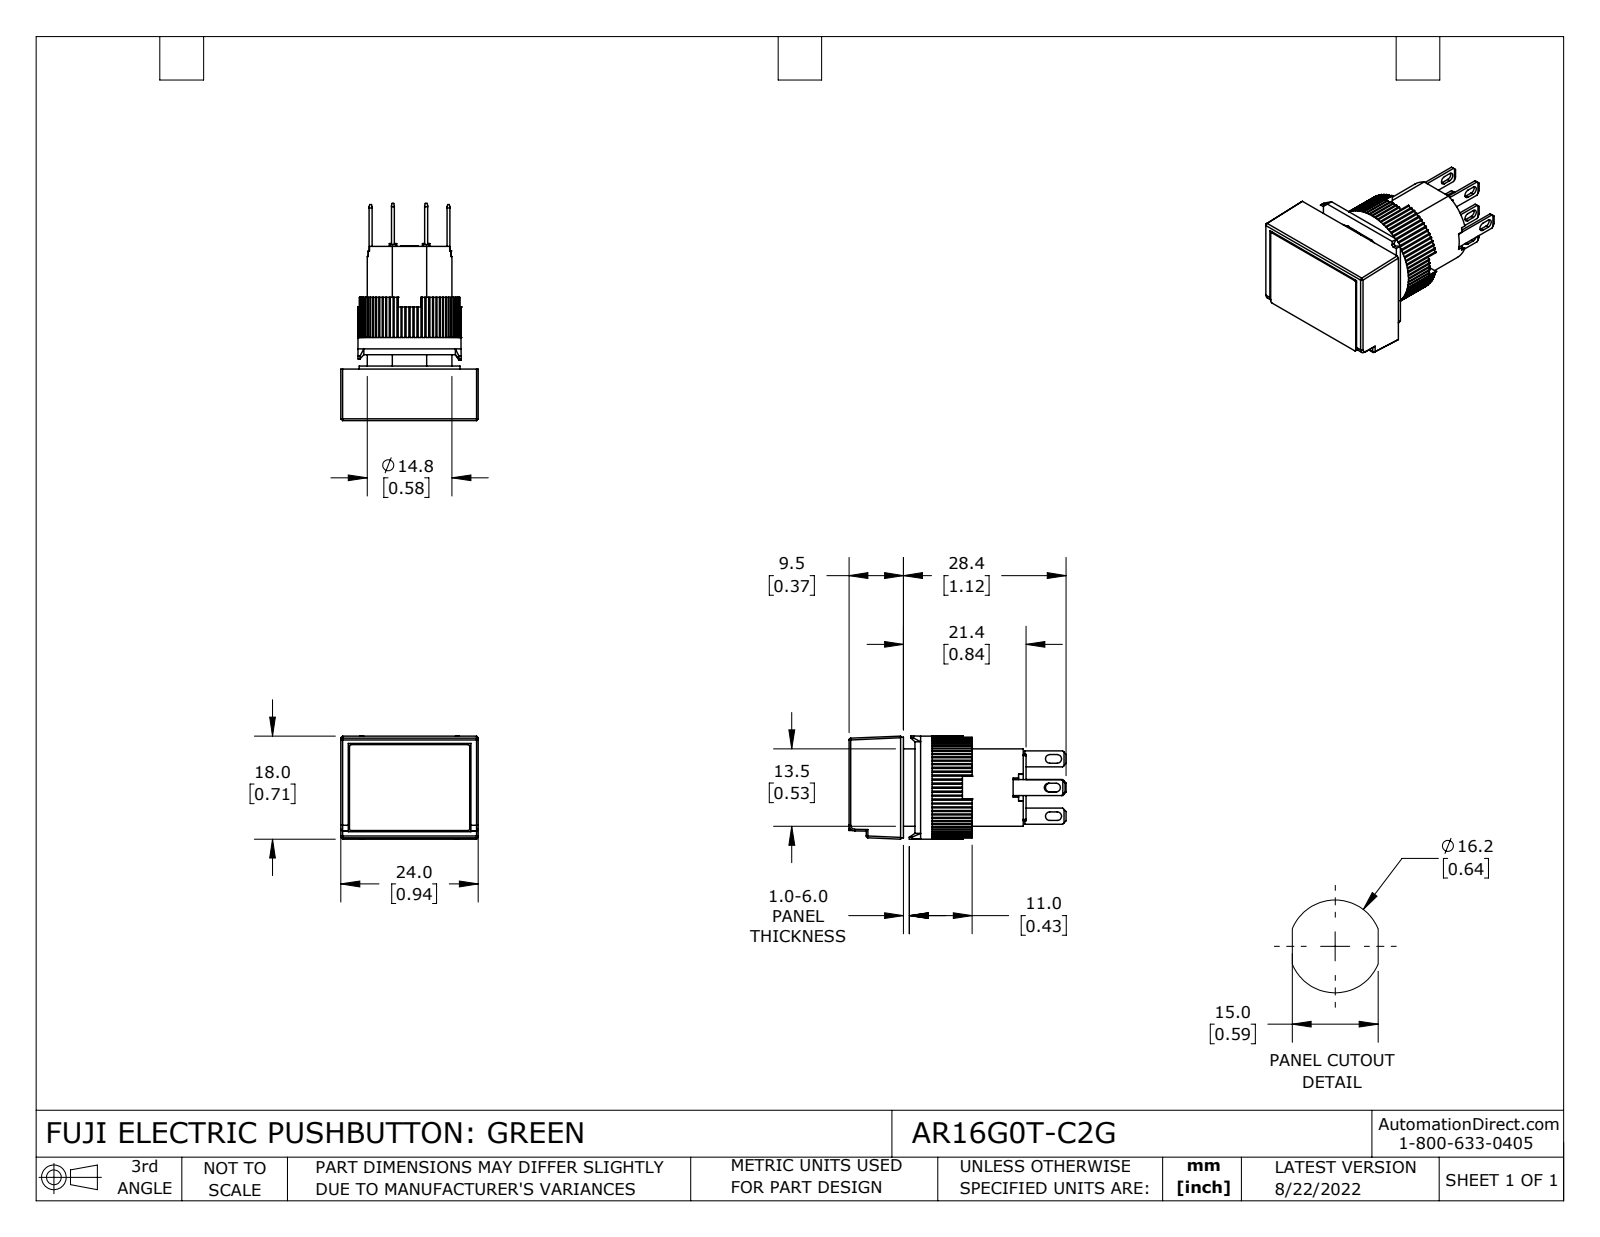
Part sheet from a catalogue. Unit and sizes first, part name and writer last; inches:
Units: inches
Overall size (bounding box): 1.492 × 0.945 × 0.709
Round holes (diameter × count): ⌀0.543 ×1, ⌀0.583 ×1
Round bosses / shafts (diameter × count): ⌀0.709 ×1, ⌀0.693 ×1
Partial cylindrical surfaces — rounded edges, fillets, slot ends (radius × count): R0.01 ×80, R0.008 ×12, R0.03 ×8, R0.012 ×6, R0.039 ×1
Main face-to-face distances: 0.213, 0.354, 0.142, 0.35, 0.492, 0.138, 0.02, 0.843, 0.059, 0.453
Volume: 0.448 in³ · Surface area: 9.503 in²
Bodies: 14 solids, 841 faces (654 planar, 181 cylindrical, 6 other)
Part name (STEP PRODUCT): AR16G0T-C2G
STEP written by: SolidWorks 2021 (CONFIG_CONTROL_DESIGN)
